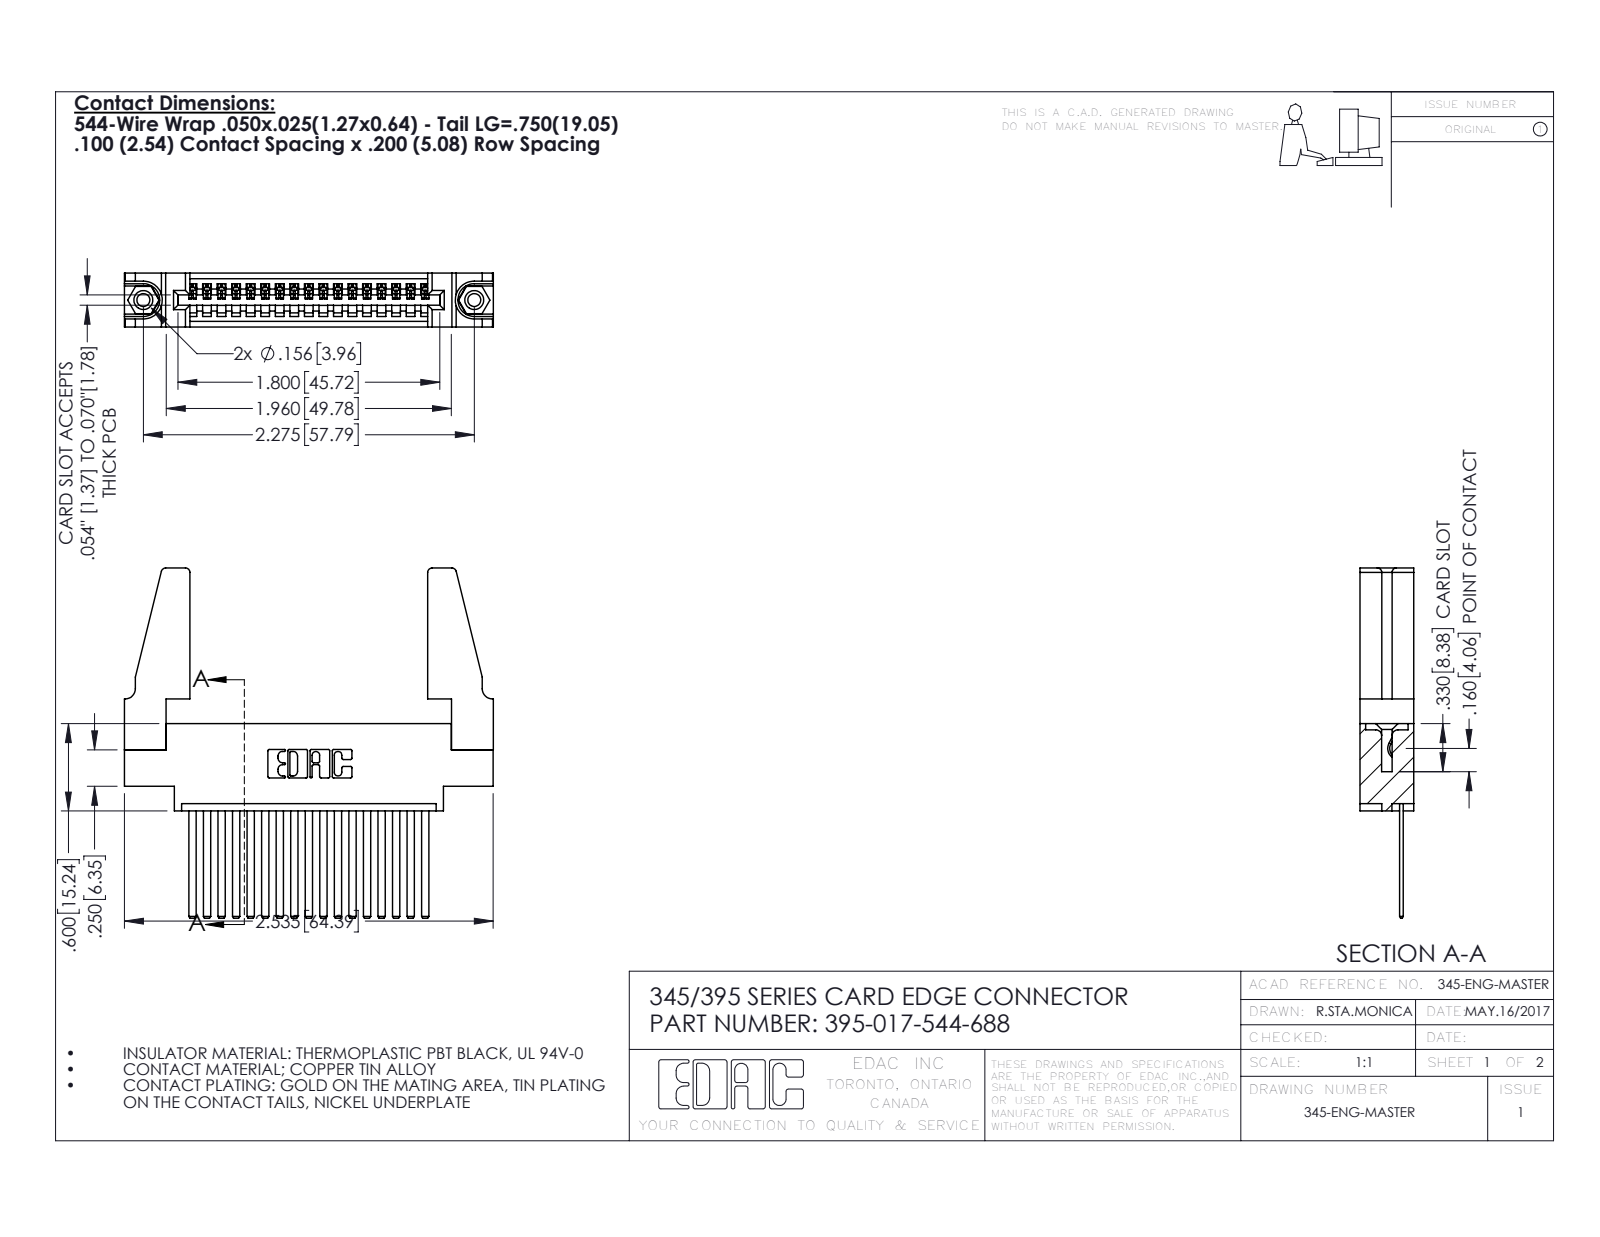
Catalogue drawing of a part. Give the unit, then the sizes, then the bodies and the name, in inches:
Units: inches
Overall size (bounding box): 2.536 × 2.407 × 0.37
Round holes (diameter × count): ⌀0.089 ×2, ⌀0.125 ×2, ⌀0.156 ×2, ⌀0.064 ×1
Round bosses / shafts (diameter × count): ⌀0.155 ×2
Partial cylindrical surfaces — rounded edges, fillets, slot ends (radius × count): R0.006 ×34, R0.01 ×22, R0.03 ×8, R0.007 ×6, R0.031 ×6, R0.026 ×3, R0.031 ×2, R0.04 ×2
Main face-to-face distances: 0.37, 0.072, 0.298, 0.098, 0.272, 0.025, 0.2, 0.225, 0.15, 0.148
Hole centre spacings: 0.27, 2.041, 2.275
Volume: 0.564 in³ · Surface area: 17.79 in²
Bodies: 22 solids, 1138 faces (768 planar, 354 cylindrical, 16 other)
Part name (STEP PRODUCT): 345-220-078_345-220-088; 395-017-544-688; 345-292-001_345-293-144; 345-250-001_345-250-001-102 (+1 more)
STEP written by: SolidWorks 2016 (CONFIG_CONTROL_DESIGN)
